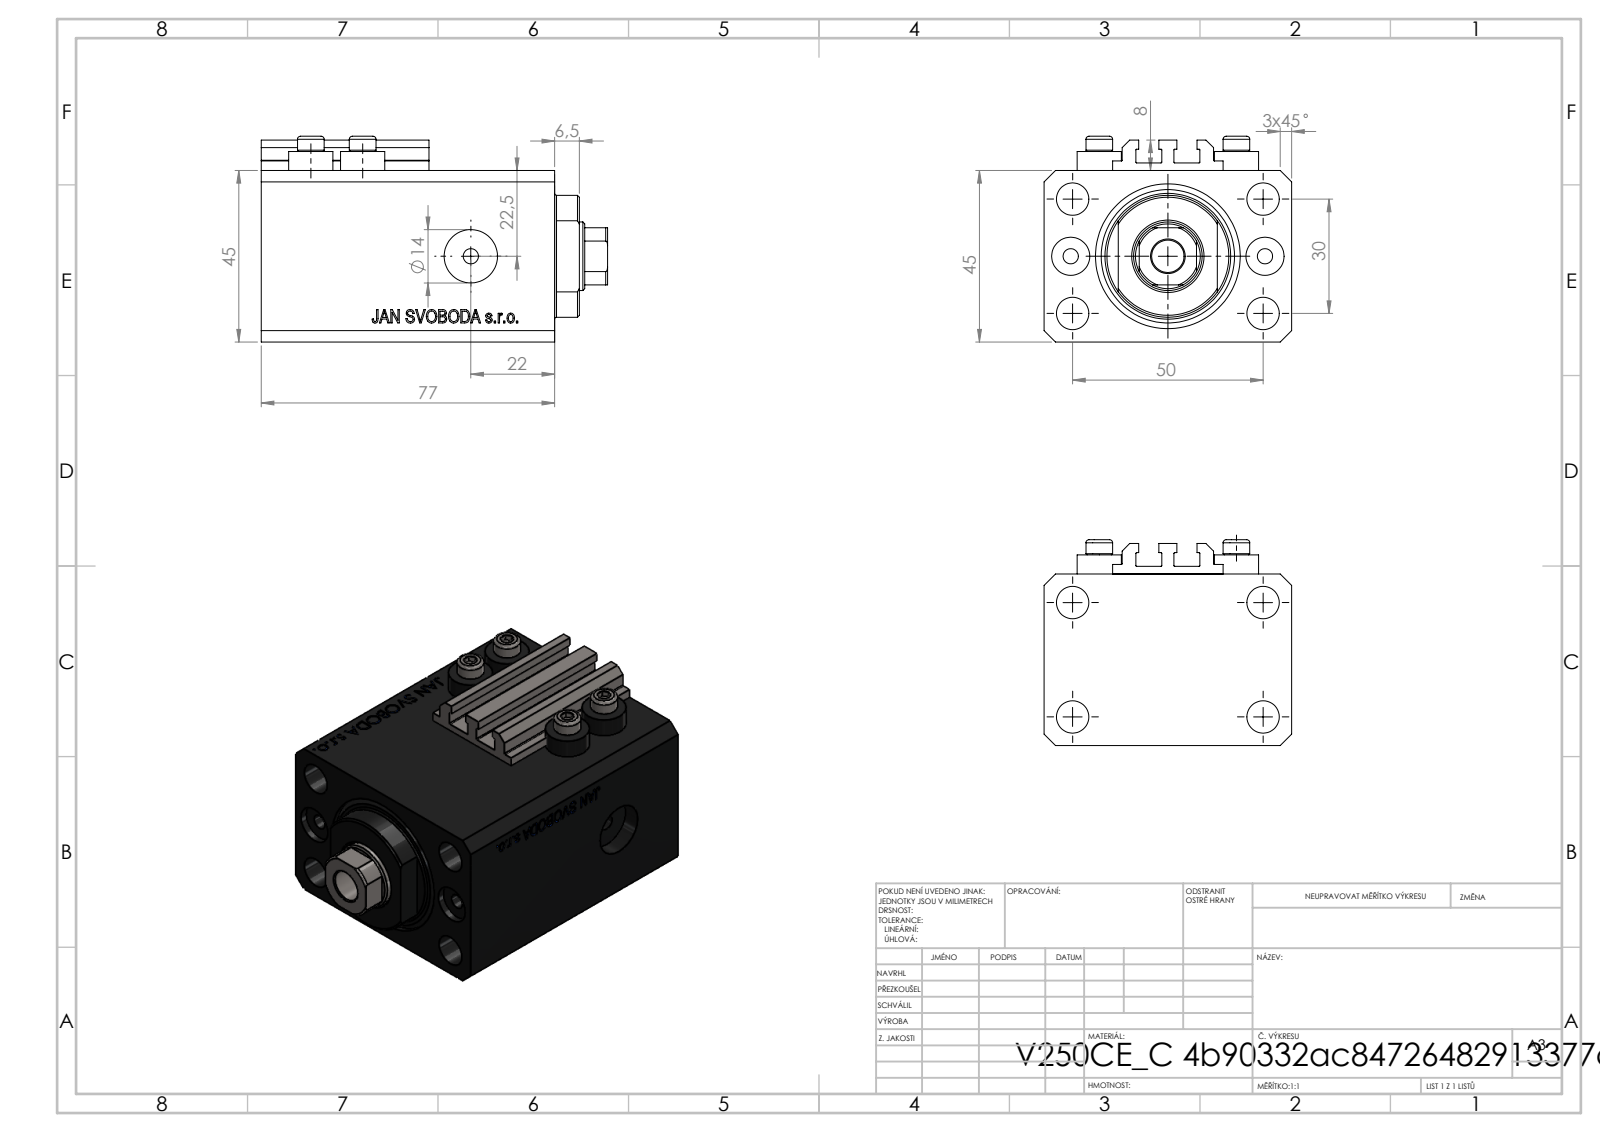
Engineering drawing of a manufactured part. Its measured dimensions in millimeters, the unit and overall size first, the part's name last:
Units: millimetres
Overall size (bounding box): 127 × 65 × 54
Round holes (diameter × count): ⌀4 ×8, ⌀8.5 ×5, ⌀10 ×2, ⌀14 ×2, ⌀18 ×1, ⌀25 ×1, ⌀38 ×1
Round bosses / shafts (diameter × count): ⌀11.6 ×4, ⌀7 ×4, ⌀6.8 ×2, ⌀6.5 ×2, ⌀4 ×2
Partial cylindrical surfaces — rounded edges, fillets, slot ends (radius × count): R0.2 ×10, R8.5 ×1, R16 ×1
Main face-to-face distances: 45, 65, 14, 63, 77, 3, 47, 6.9, 56.1, 70.1
Hole centre spacings: 15.01, 29.15, 52.68, 13.6, 25.5, 30, 36, 38.48
Volume: 215 512 mm³ · Surface area: 60 016 mm²
Bodies: 10 solids, 1086 faces (536 planar, 98 cylindrical, 452 other)
Part name (STEP PRODUCT): V250CE_C_Body; V250CE_VC_C; SWITCH_V250CE; ALLEN BOLT V250CE (+1 more)
STEP written by: SolidWorks 2019 (CONFIG_CONTROL_DESIGN)
